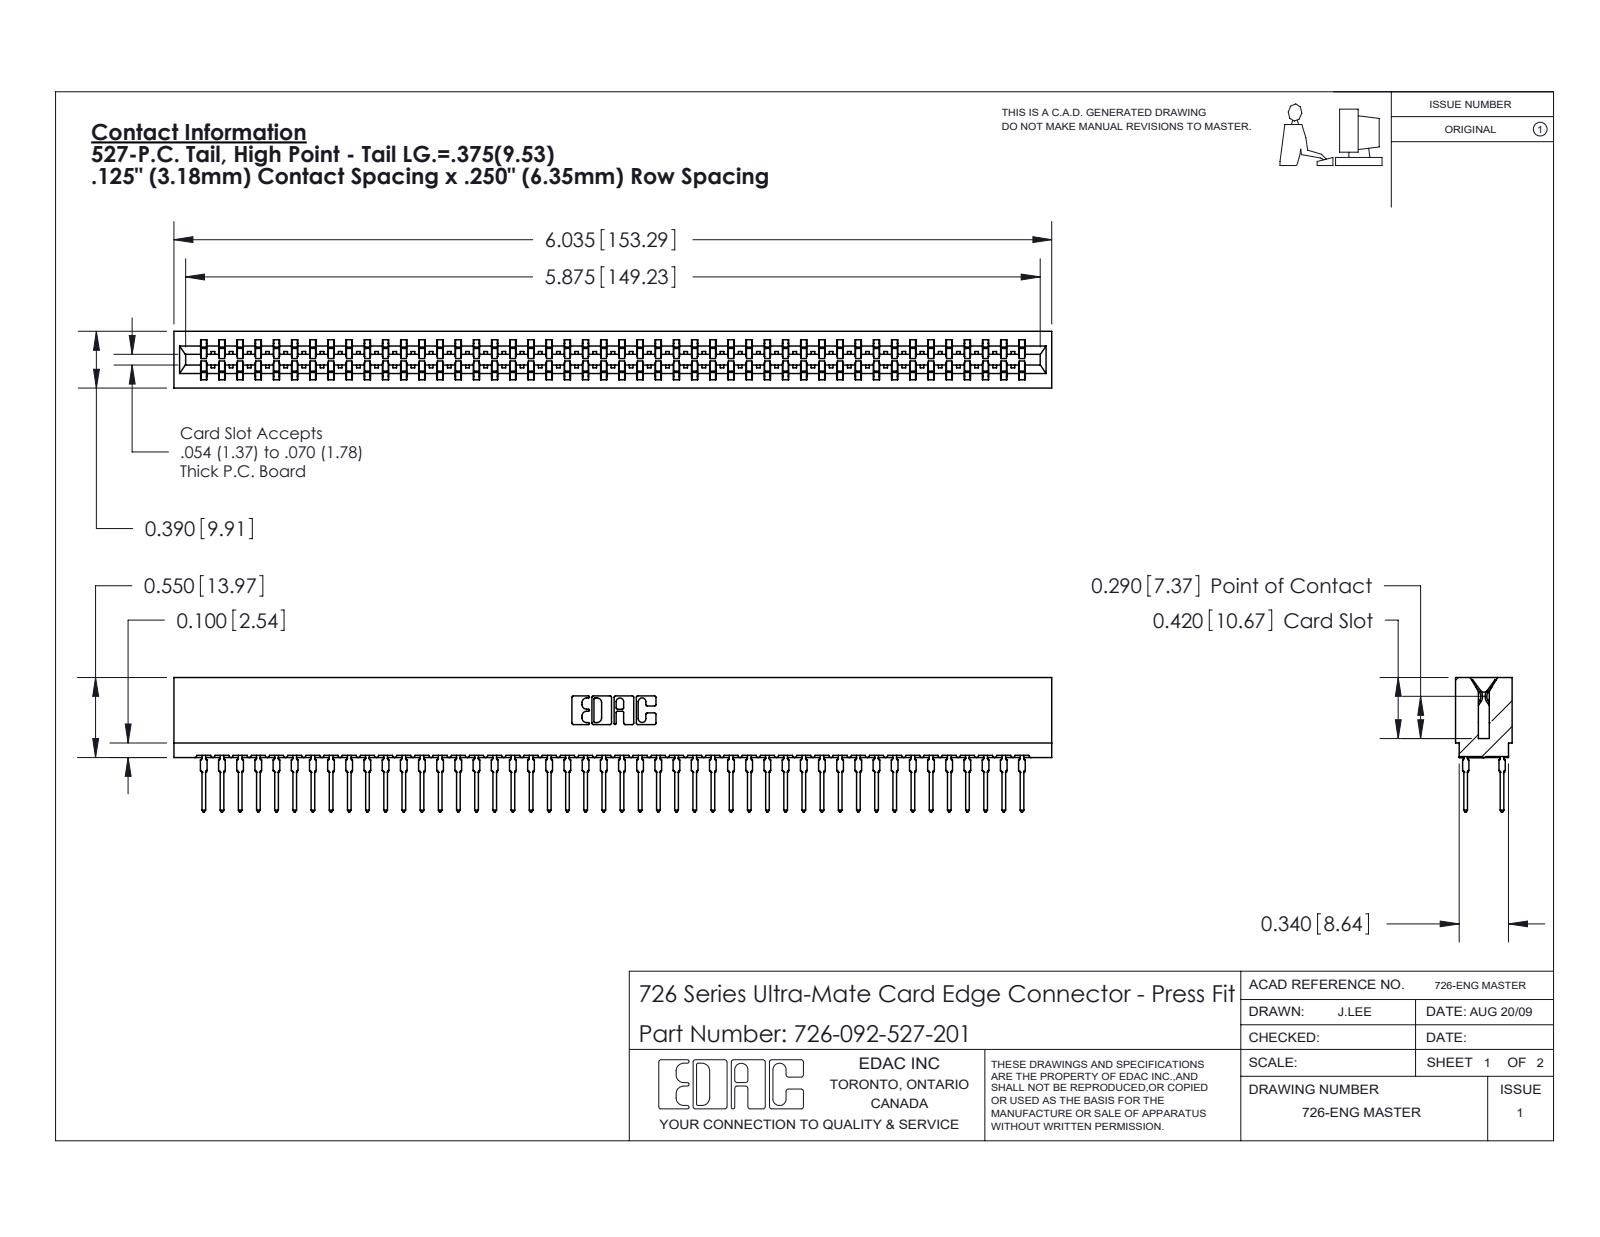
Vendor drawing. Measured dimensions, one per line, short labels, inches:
name: 746-292-001_527; 726-092-527-201; 726 Part_.515 Slot Depth - 01
written by: SolidWorks 2020 (CONFIG_CONTROL_DESIGN)
unit: in
bodies: 92 solids, 8331 faces (4287 planar, 1652 cylindrical, 2392 other)
size: 6.035 × 0.924 × 0.39
volume: 0.064 in³; area: 38.01 in²
rounds: 184× R0.021, 47× R0.015, 22× R0.01, 8× R0.005, 8× R0.011, 6× R0.007, 6× R0.031, 3× R0.026
face distances: 0.057, 0.333, 0.025, 0.307, 0.39, 0.25, 0.275, 0.083, 0.365, 0.032
